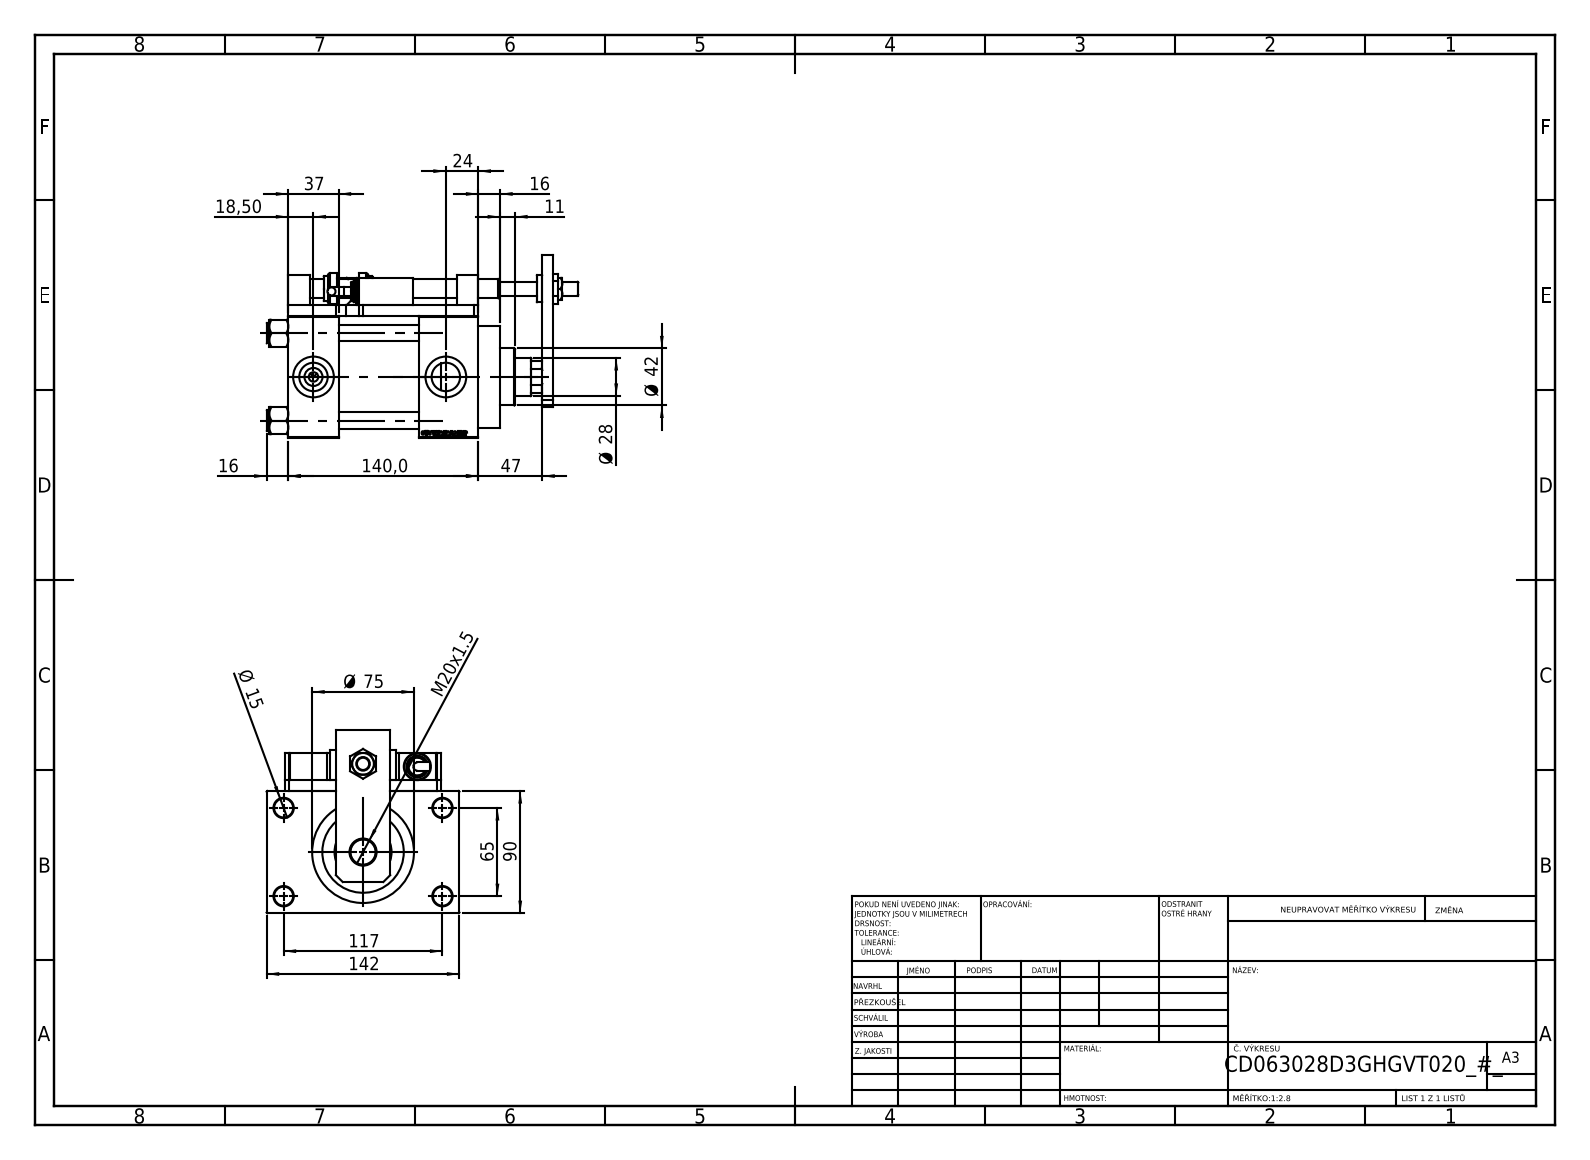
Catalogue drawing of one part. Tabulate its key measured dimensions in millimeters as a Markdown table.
| quantity | value |
| --- | --- |
| part name | V215CD_SWITCH_Q_DIMA; V215CD_SWITCH_Q_MAGNET; V215CD_D_Body; V215CD_SWITCH_Q_NUT10 (+8 more) |
| STEP written by | SolidWorks 2019 (CONFIG_CONTROL_DESIGN) |
| units | millimeters |
| bodies | 26 solids, 1432 faces (666 planar, 167 cylindrical, 599 other) |
| overall size | 229.5 × 142 × 135 |
| volume | 1 356 000 mm³ |
| surface area | 290 182 mm² |
| round holes (diameter × count) | 14 × 5, 8.5 × 4, 12 × 4, 13.5 × 4, 20.96 × 4, 30 × 4, 7 × 3, 10 × 1, 18.5 × 1, 20 × 1, 28 × 1, 31 × 1 |
| round bosses / shafts (diameter × count) | 15 × 4, 20 × 3, 16 × 2, 14 × 2, 6 × 2, 75 × 1, 69 × 1, 42 × 1 |
| partial cylindrical surfaces (radius × count) | 7.5 × 4, 13.5 × 1 |
| main face-to-face distances | 8, 90, 44, 140, 37, 103, 98, 59, 96, 16 |
| hole center spacings | 66.92, 26.35, 45.47, 64.3, 69.81, 90.65, 111.34, 65 |
